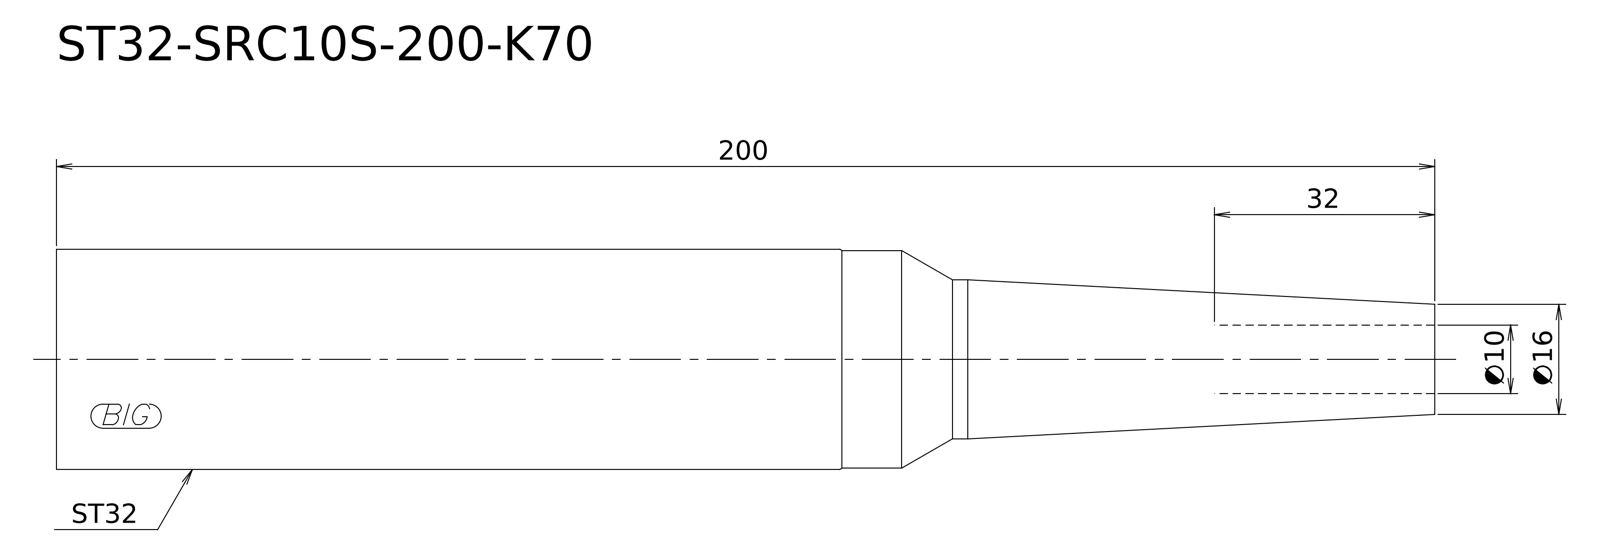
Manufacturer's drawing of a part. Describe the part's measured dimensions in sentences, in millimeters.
Its 3-D file was written by "Kubotek KeyCreator V8.5.1 (14335) (CONFIG_CONTROL_DESIGN)". It is 1 solid with 8 faces: 2 planar, 3 cylindrical and 3 other. Overall it measures 200 by 32 by 32 millimeters. Its volume is 124 311 cubic millimeters and its surface area 18 388 square millimeters. Round bosses or shafts: 1 of diameter 32, 1 of diameter 31.6, 1 of diameter 23.1. The main face-to-face distances are 200.
